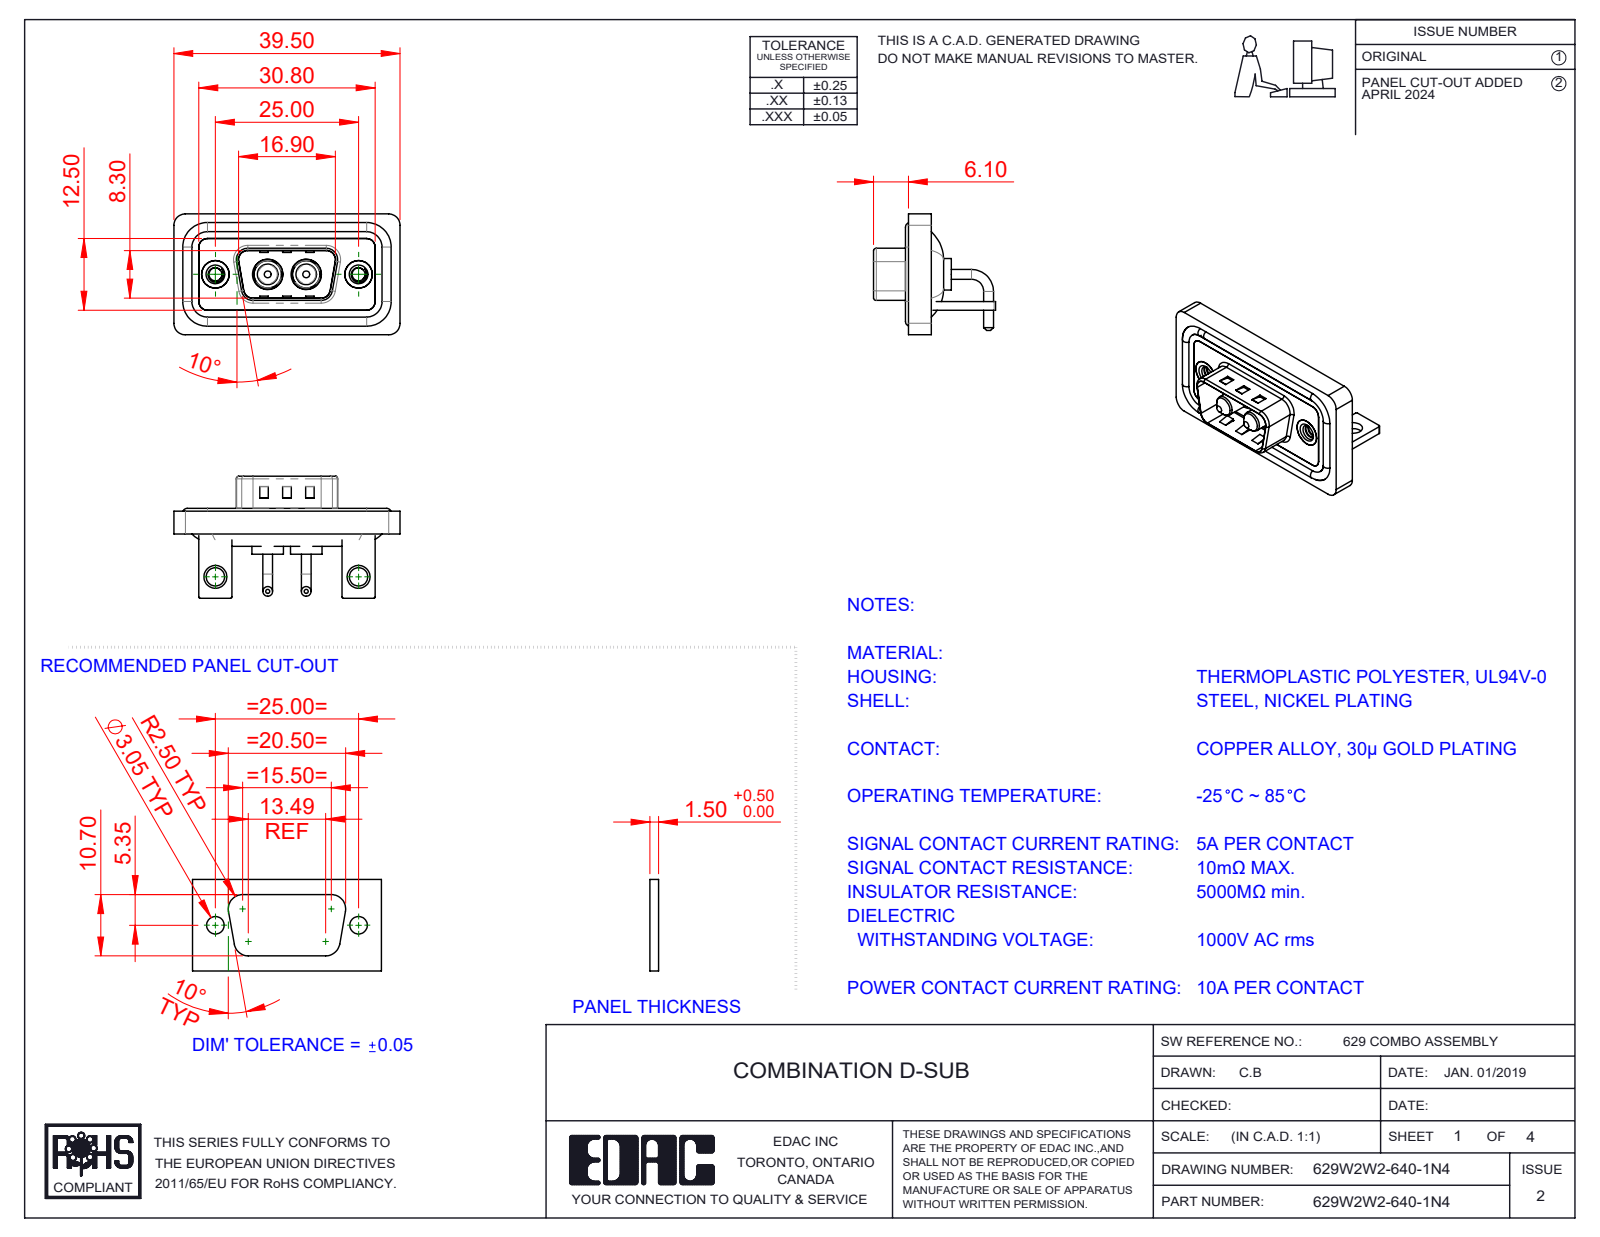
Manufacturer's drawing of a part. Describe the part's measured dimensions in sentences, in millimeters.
The part is named "629Combo Shell Front_09 Contacts; 629Combo Threaded Rivet_3; 629Combo Housing_2W2; Power Pin_10A RA (+4 more)". Its 3-D file was written by "SolidWorks 2023 (CONFIG_CONTROL_DESIGN)". It is 13 solids with 537 faces: 185 planar, 240 cylindrical and 112 other. Overall it measures 39.5 by 21.3 by 21.1 millimeters. Its volume is 4 746 cubic millimeters and its surface area 7 652 square millimeters. Round holes: 2 of diameter 2.26, 2 of diameter 3.2, 2 of diameter 4, 2 of diameter 4.8, 2 of diameter 4.85, 2 of diameter 5, 2 of diameter 5.3. Round bosses or shafts: 4 of diameter 1.7, 4 of diameter 1.6, 2 of diameter 5.5, 2 of diameter 5.2, 2 of diameter 4.9, 2 of diameter 4.75, 2 of diameter 3.75, 2 of diameter 3.6. Partial cylindrical surfaces (rounded edges, fillets, slot ends): 19 of radius 2, 18 of radius 1.5, 16 of radius 0.25, 9 of radius 0.5, 8 of radius 1.6, 4 of radius 0.6, 4 of radius 0.65, 4 of radius 0.9. The main face-to-face distances are 0.4, 1.5, 2.9, 0.8, 1.1, 1.2, 2.1, 1.6, 3.7, 2.5. The hole center spacings are 9.14, 15.86, 25, 6.72.
